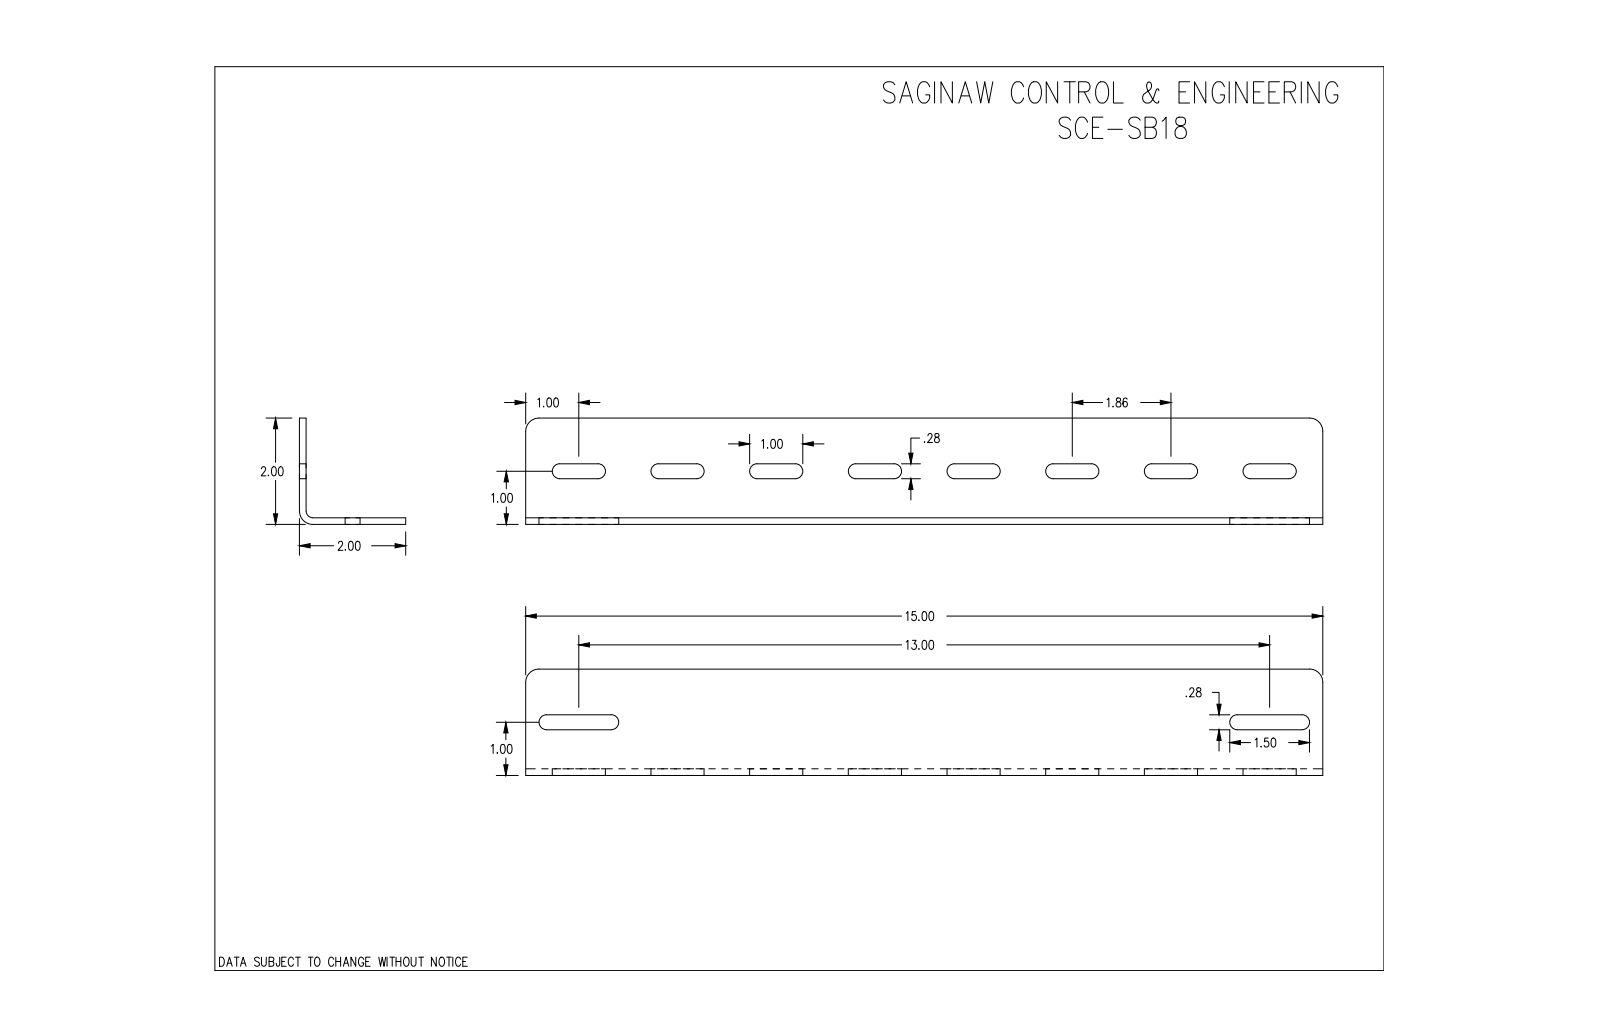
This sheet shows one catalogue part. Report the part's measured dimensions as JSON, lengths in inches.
{"part_name": "SCE-SB18", "step_written_by": "SolidWorks 2019 (CONFIG_CONTROL_DESIGN)", "units": "inches", "bodies": {"solids": 2, "faces": 108, "planar": 56, "cylindrical": 52, "other": 0}, "overall_size": [22.094, 15, 2], "volume_in3": 13.49, "surface_area_in2": 231.4, "partial_cylinders_radius": [[0.141, 36], [0.25, 8], [0.125, 2]], "face_to_face_distances": [0.125, 0.125, 21.969, 22.094, 21.844, 21.969, 2, 1.875, 20.094, 0.859]}
